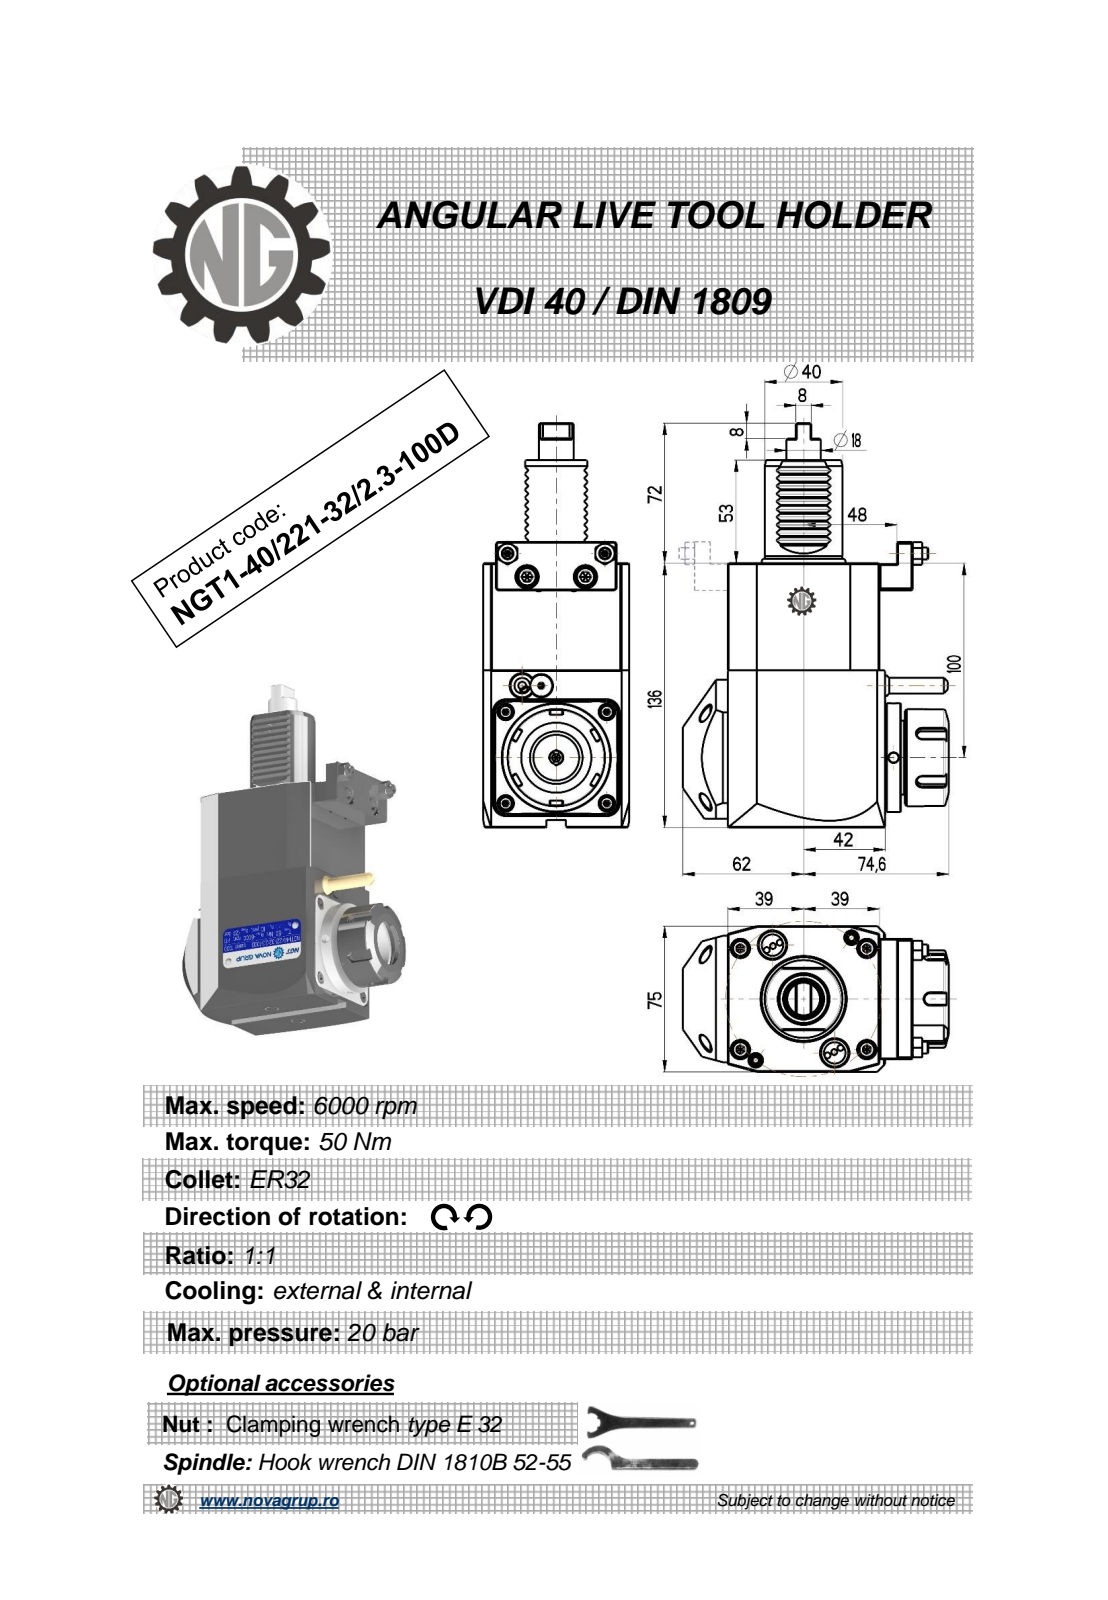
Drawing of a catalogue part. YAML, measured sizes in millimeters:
part_name: "NGT1_40_221_32_2_3_100D"
step_written_by: "PRO/ENGINEER BY PARAMETRIC TECHNOLOGY CORPORATION, 2010280 (CONFIG_CONTROL_DESIGN)"
units: millimeters
bodies: {solids: 1, faces: 439, planar: 210, cylindrical: 86, other: 143}
overall_size: [208, 136.6, 75]
volume: 1009000
surface_area: 79672
round_holes:
  - {diameter: 5, count: 3}
  - {diameter: 3, count: 1}
  - {diameter: 27, count: 1}
  - {diameter: 42, count: 1}
round_bosses_or_shafts:
  - {diameter: 6, count: 2}
  - {diameter: 56, count: 1}
  - {diameter: 50, count: 1}
  - {diameter: 41.4, count: 1}
  - {diameter: 41, count: 1}
  - {diameter: 40, count: 1}
  - {diameter: 17.8, count: 1}
  - {diameter: 11.2, count: 1}
partial_cylinders:
  - {radius: 0.3, count: 20}
  - {radius: 0.31, count: 10}
  - {radius: 0.22, count: 6}
  - {radius: 3, count: 5}
  - {radius: 0.8, count: 2}
  - {radius: 40, count: 1}
face_to_face_distances: [75, 136, 78, 14, 81, 0.5, 11, 3, 8, 6]
hole_center_spacings: [40.93]
